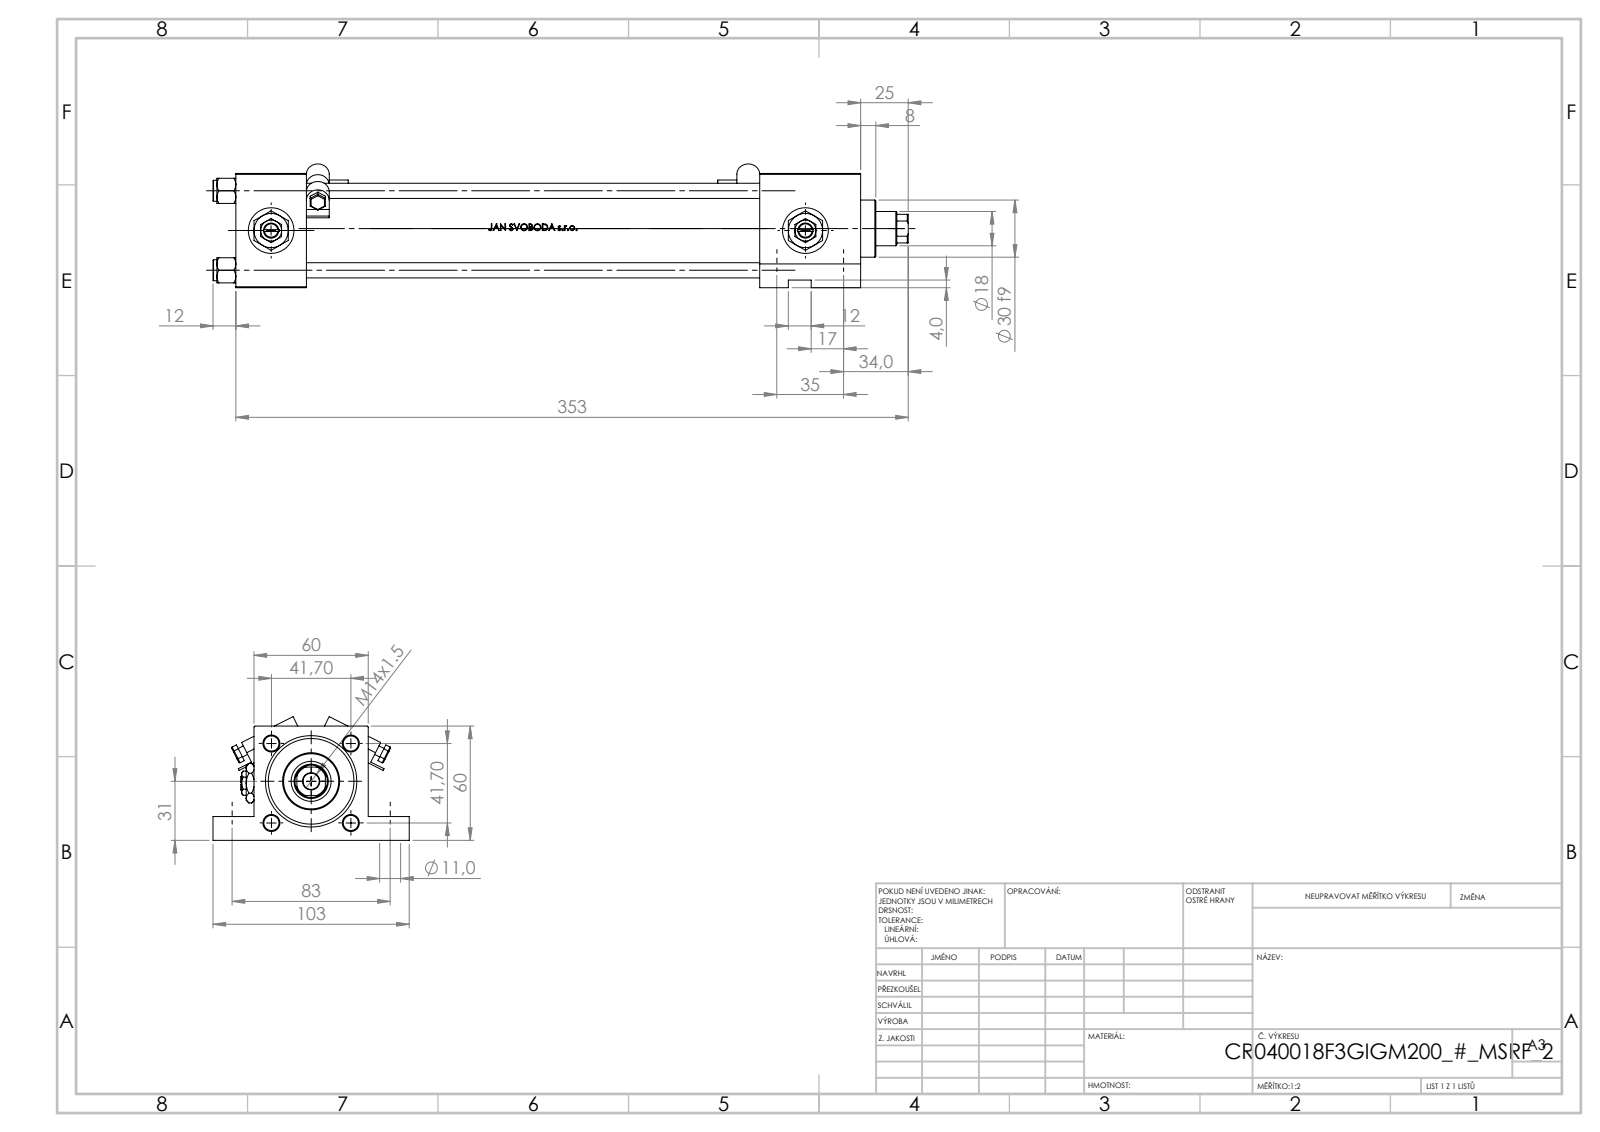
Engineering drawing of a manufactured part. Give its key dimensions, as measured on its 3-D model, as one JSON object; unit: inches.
{"part_name": "NUT_M5_F; V215CR_VCP_F; MSRF_MSRG1; V215CR_F_Body (+3 more)", "step_written_by": "SolidWorks 2019 (CONFIG_CONTROL_DESIGN)", "units": "inches", "bodies": {"solids": 15, "faces": 1279, "planar": 520, "cylindrical": 177, "other": 582}, "overall_size": [14.37, 4.055, 2.558], "volume_in3": 35.54, "surface_area_in2": 303.3, "round_holes": [[0.315, 4], [0.433, 4], [0.656, 3], [0.945, 3], [0.276, 2], [0.335, 1], [0.63, 1], [0.709, 1], [0.827, 1], [1.22, 1], [1.575, 1], [1.772, 1]], "round_bosses_or_shafts": [[0.433, 4], [0.197, 2], [0.098, 2], [1.811, 1], [1.181, 1]], "partial_cylinders_radius": [[0.02, 12], [0.236, 4], [0.335, 1]], "face_to_face_distances": [2.362, 1.457, 12.913, 10.827, 2.087, 11.457, 9.37, 11.783, 10.327, 0.957], "hole_center_spacings": [1.642, 1.133, 1.189, 1.378, 1.657, 1.971, 2.322, 3.268]}
